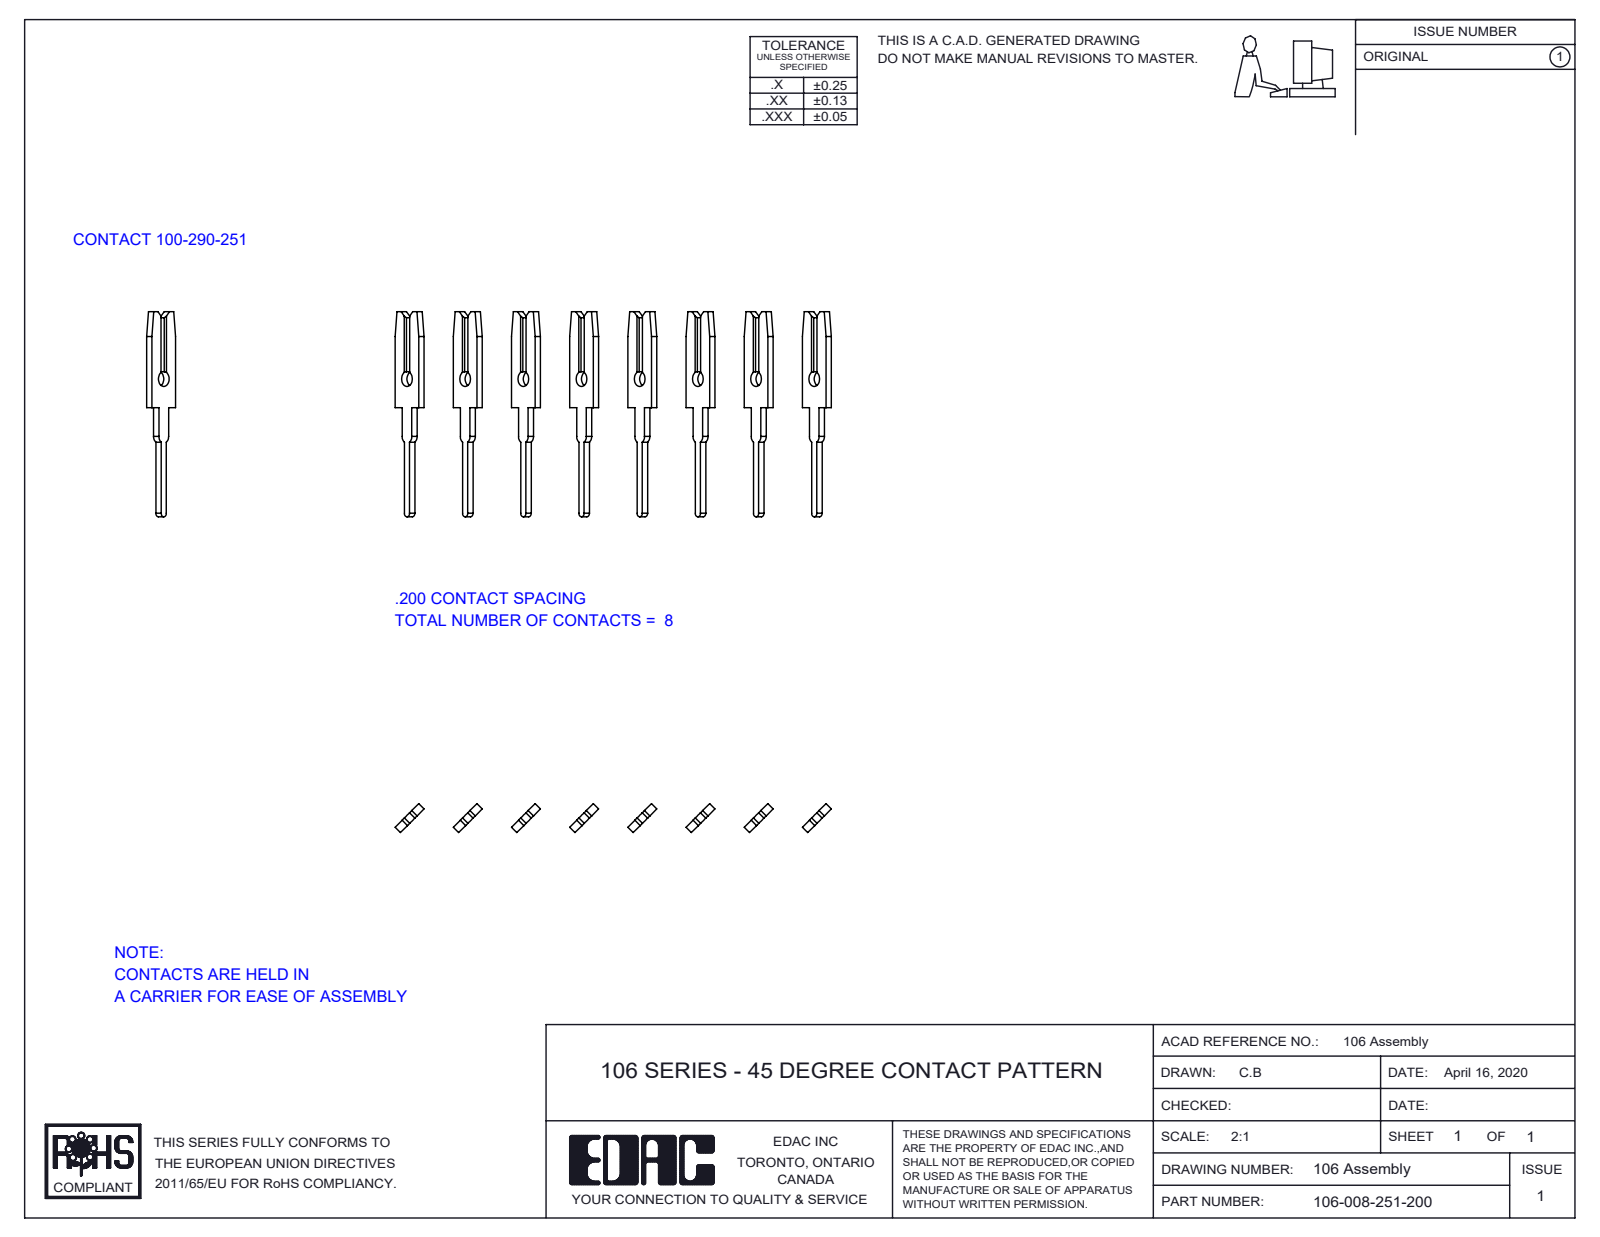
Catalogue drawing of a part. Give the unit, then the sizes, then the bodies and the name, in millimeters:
Units: millimetres
Overall size (bounding box): 38.1 × 17.9 × 2.5
Round holes (diameter × count): ⌀1.3 ×8
Partial cylindrical surfaces — rounded edges, fillets, slot ends (radius × count): R0.3 ×8, R0.6 ×8
Main face-to-face distances: 3.6, 7.2, 0.7, 14.4, 18, 10.8, 2.9, 4.2, 10.8, 21.5
Hole centre spacings: 3.6, 10.8, 7.2, 14.4, 18, 7.2, 21.6, 3.6
Volume: 100 mm³ · Surface area: 719 mm²
Bodies: 8 solids, 224 faces (176 planar, 48 cylindrical, 0 other)
Part name (STEP PRODUCT): 106-008-251-200; 100-290-001_100-290-251
STEP written by: SolidWorks 2016 (CONFIG_CONTROL_DESIGN)
